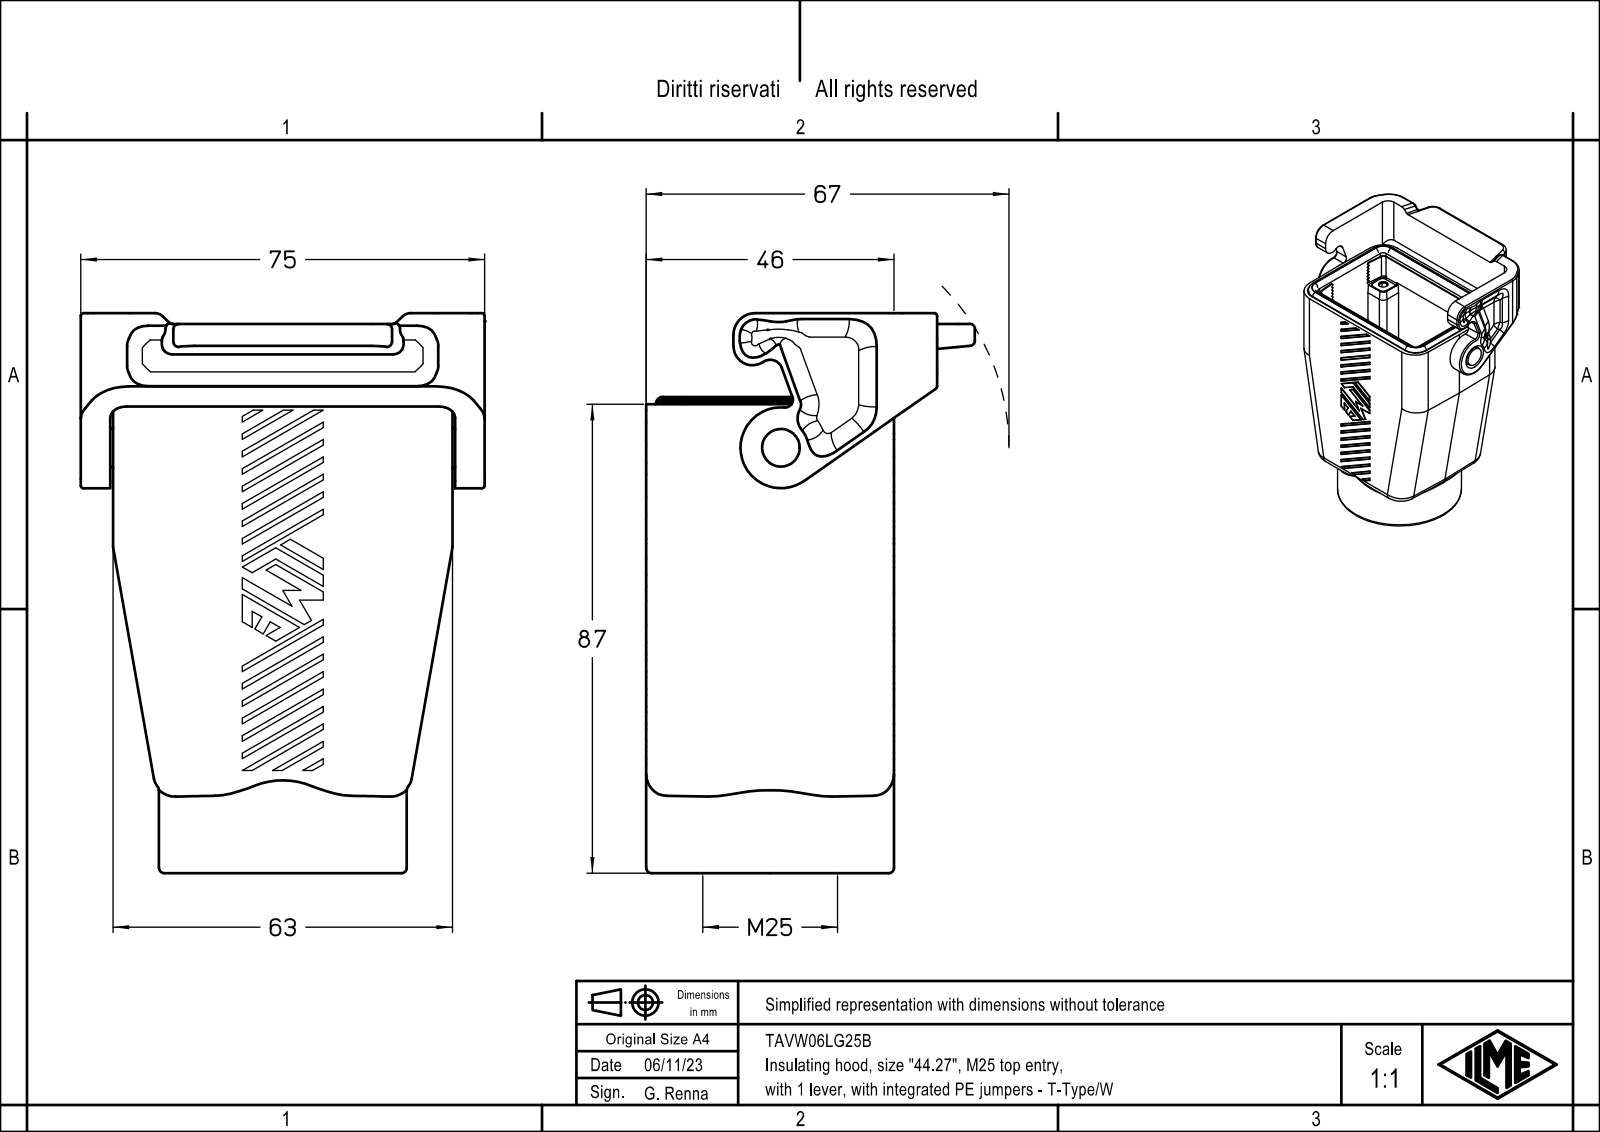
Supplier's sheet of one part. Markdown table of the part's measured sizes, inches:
| quantity | value |
| --- | --- |
| part name | TAVW06LG25B |
| STEP written by | Creo Elements/Direct Modeling 20.1B 02-Apr-2019 (C) Parametric Technology GmbH (AUTOMOTIVE_DESIGN) |
| units | inches |
| bodies | 1 solid, 708 faces (312 planar, 344 cylindrical, 52 other) |
| overall size | 4.091 × 2.953 × 2.407 |
| volume | 7.133 in³ |
| surface area | 66.88 in² |
| round holes (diameter × count) | 0.138 × 4, 0.827 × 1, 0.929 × 1 |
| round bosses / shafts (diameter × count) | 1.811 × 1, 0.276 × 1 |
| partial cylindrical surfaces (radius × count) | 0.006 × 128, 0.059 × 15, 0.079 × 14, 0.118 × 13, 0.051 × 12, 0.039 × 8, 0.276 × 8, 0.063 × 4 |
| main face-to-face distances | 0.213, 1.598, 1.811, 1.386, 0.232, 2.287, 0.118, 0.807, 0.331, 1.929 |
| hole center spacings | 1.016, 1.063, 1.732, 2.032 |
